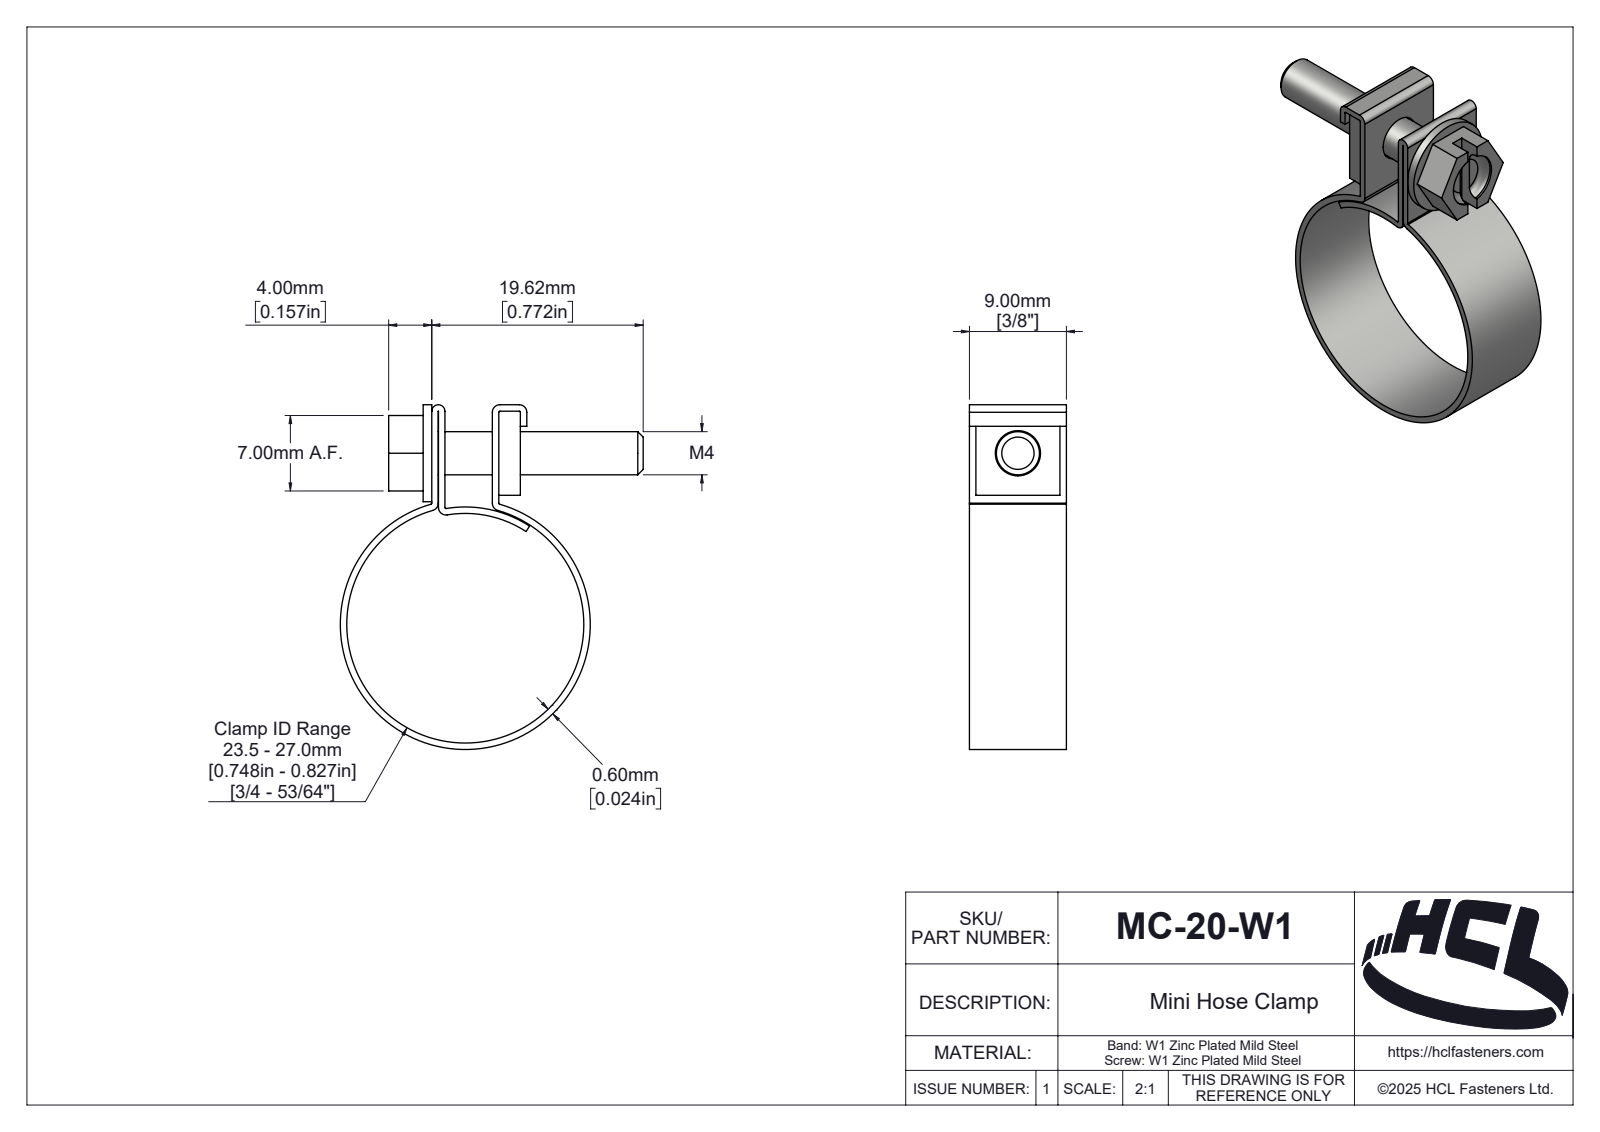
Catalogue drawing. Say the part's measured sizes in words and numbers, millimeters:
The part is named "MC-20-W1". Its 3-D file was written by "SolidWorks 2025 (AUTOMOTIVE_DESIGN)". It is 3 solids with 175 faces: 38 planar, 84 cylindrical and 53 other. Overall it measures 31.98 by 28.11 by 9 millimeters. Its volume is 1 041 cubic millimeters and its surface area 2 656 square millimeters. Round holes: 1 of diameter 4.2, 1 of diameter 5, 1 of diameter 22. Round bosses or shafts: 1 of diameter 23.2, 1 of diameter 9, 1 of diameter 4. Partial cylindrical surfaces (rounded edges, fillets, slot ends): 5 of radius 0.1, 5 of radius 0.7, 1 of radius 0.2, 1 of radius 0.61, 1 of radius 0.81, 1 of radius 1.01, 1 of radius 1.06, 1 of radius 1.28. The main face-to-face distances are 0.6, 0.62, 5, 5.62, 6.22, 7, 2, 2.6, 8.22, 7.6.
